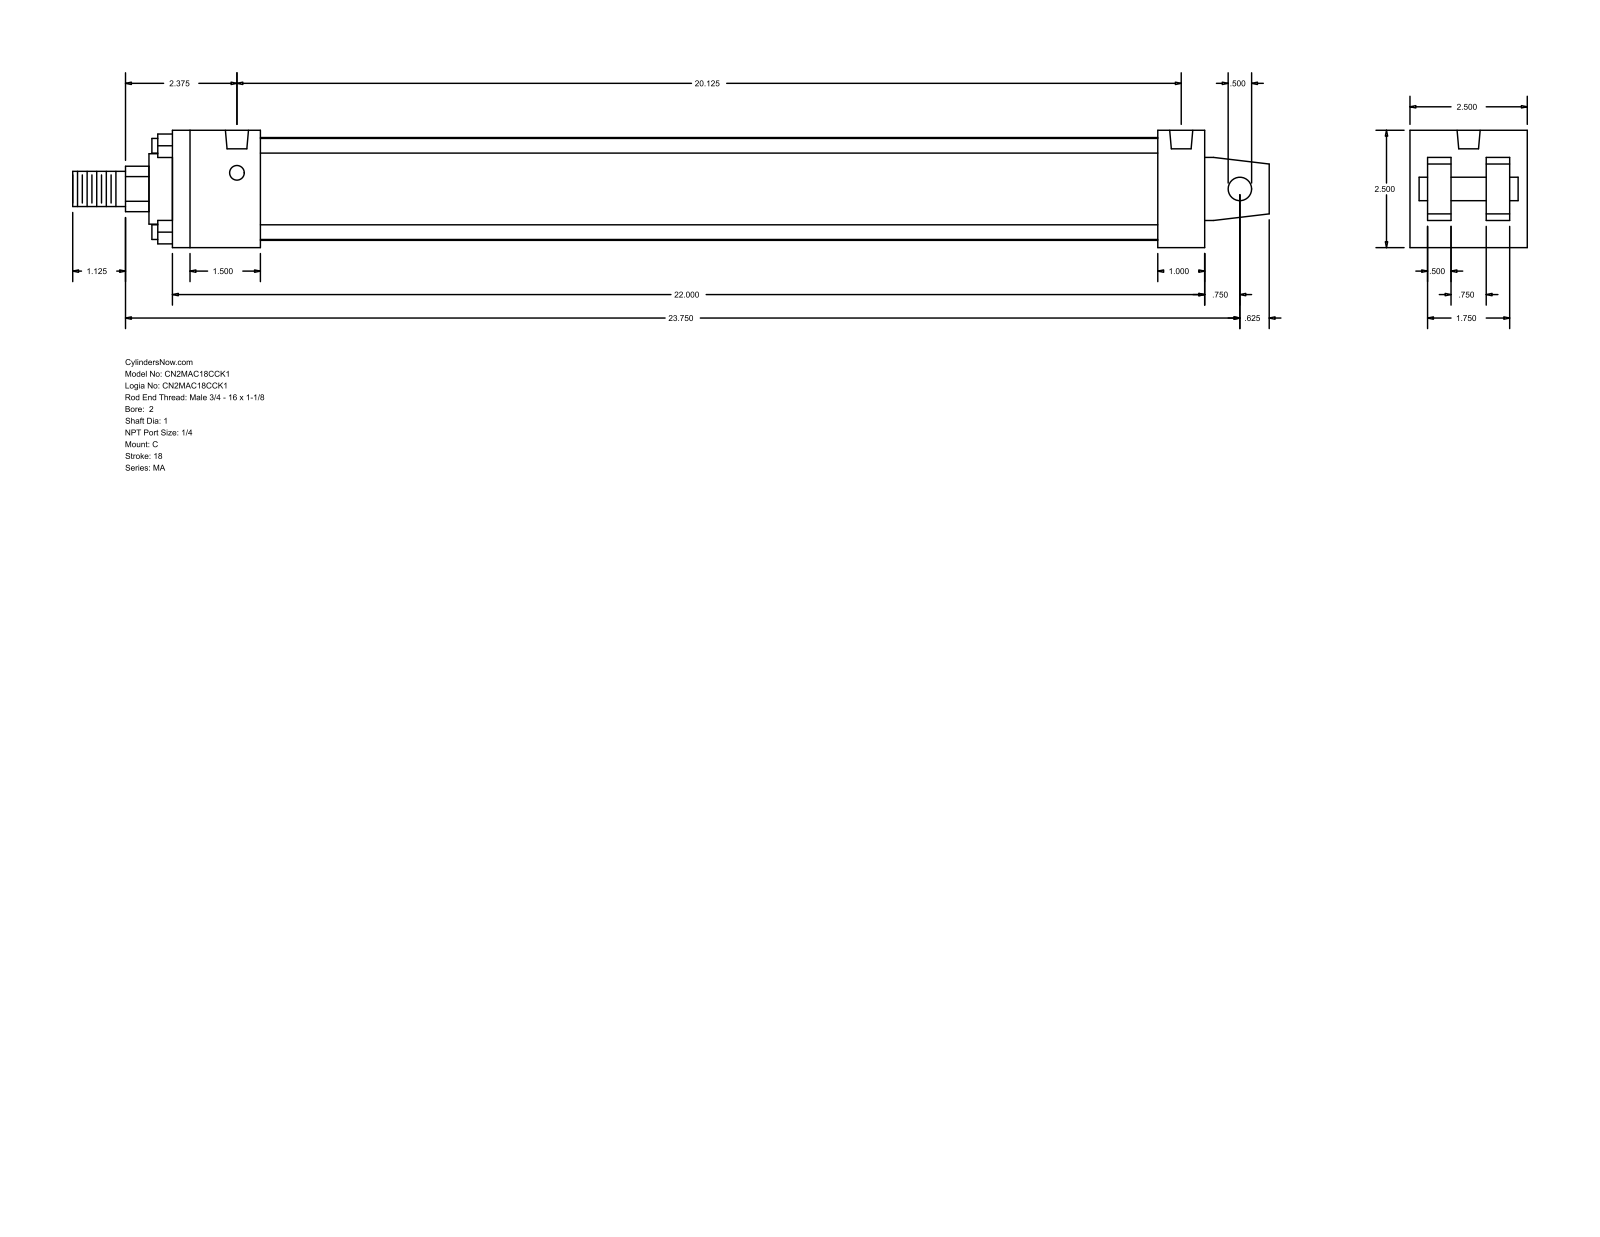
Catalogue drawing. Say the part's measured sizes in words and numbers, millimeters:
The part is named "MA_C__0200_1". Its 3-D file was written by "GSSL Pune (CONFIG_CONTROL_DESIGN)". It is 0 solids with 103 faces: 76 planar, 27 cylindrical and 0 other. Overall it measures 647.7 by 63.5 by 63.5 millimeters. Round holes: 4 of diameter 7.94, 2 of diameter 12.49. Round bosses or shafts: 4 of diameter 7.94, 1 of diameter 55.63, 1 of diameter 38.1, 1 of diameter 25.4, 1 of diameter 19.05, 1 of diameter 12.7. Partial cylindrical surfaces (rounded edges, fillets, slot ends): 1 of radius 12.29. The main face-to-face distances are 63.5, 12.7, 558.8, 22.22, 41.28, 9.52, 53.98, 31.76, 47.63, 25.4. The hole center spacings are 511.17.
